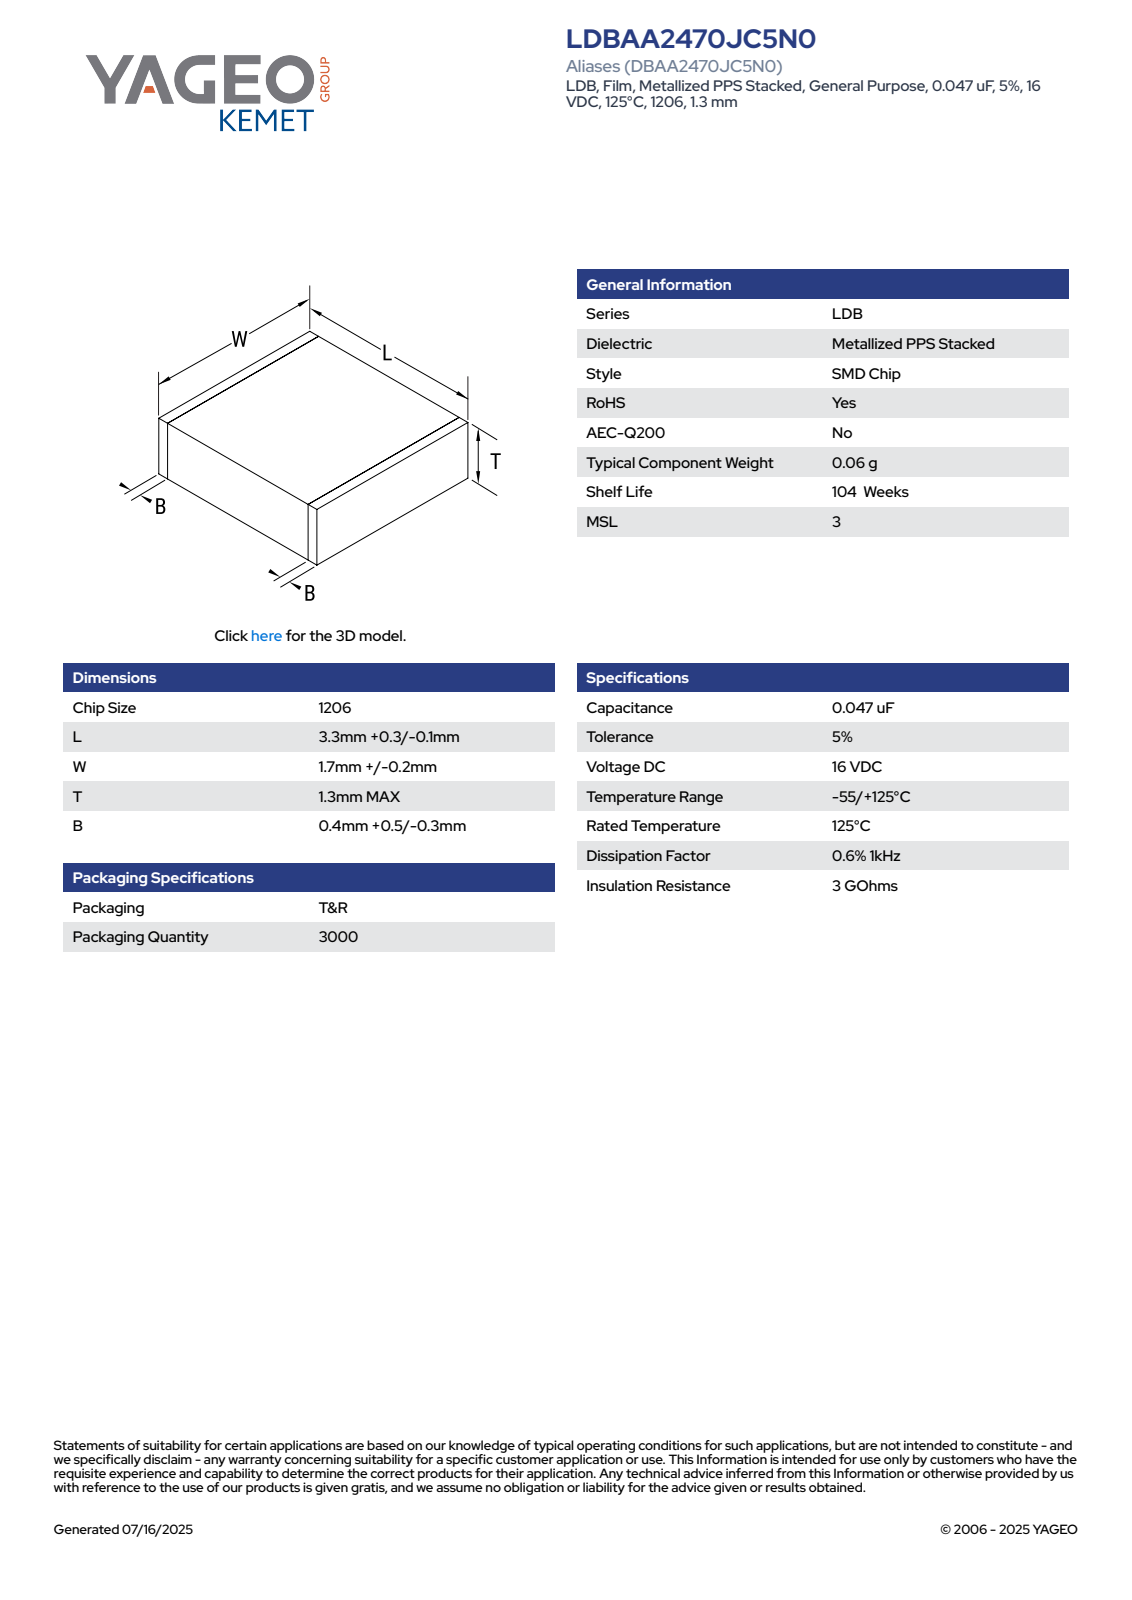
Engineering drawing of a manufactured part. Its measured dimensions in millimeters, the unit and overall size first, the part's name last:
Units: millimetres
Overall size (bounding box): 3.6 × 1.9 × 1.3
Main face-to-face distances: 1.28, 1.29, 1.88, 1.89, 3.6, 1.3, 1.9, 0.5, 3.1, 2.6
Volume: 9 mm³ · Surface area: 29 mm²
Bodies: 4 solids, 73 faces (73 planar, 0 cylindrical, 0 other)
Part name (STEP PRODUCT): CFS_LDELDB_1206_L3.6W1.9T1.3B0.9
STEP written by: SolidWorks 2020 (AUTOMOTIVE_DESIGN)
